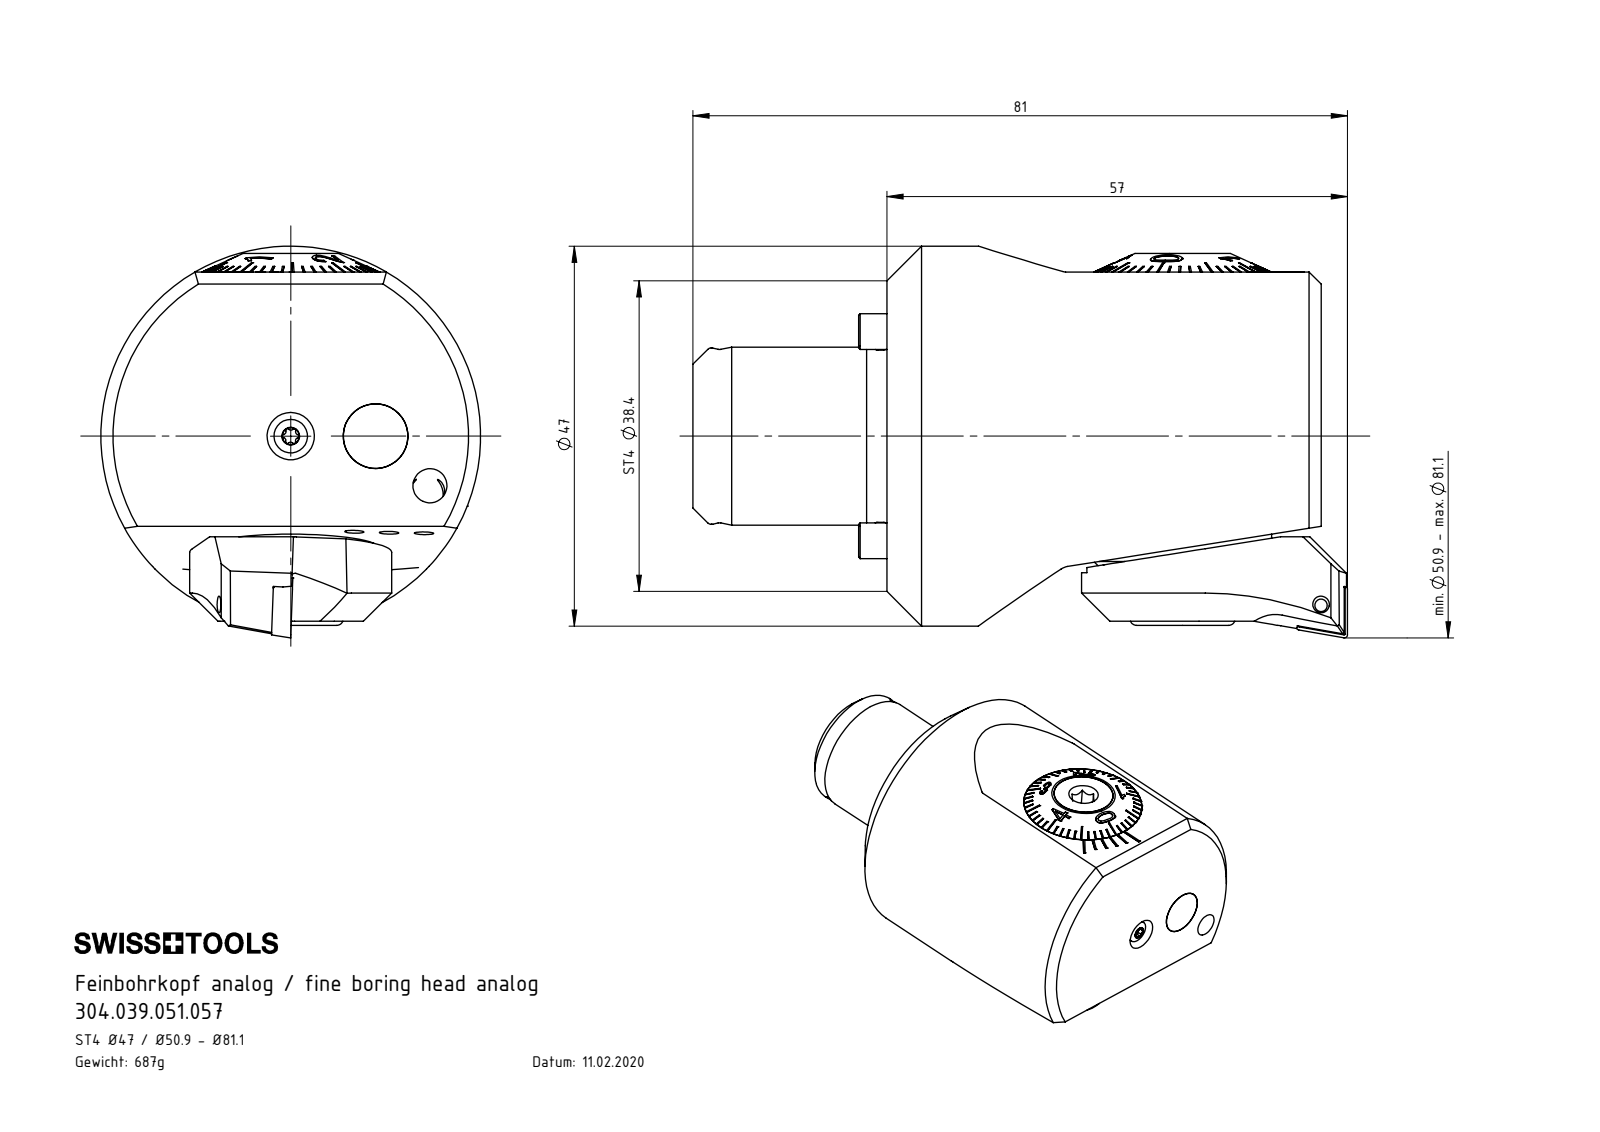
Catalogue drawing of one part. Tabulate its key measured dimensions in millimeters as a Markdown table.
| quantity | value |
| --- | --- |
| part name | F42-BG1.AA4.022; F42-BG2.014.014_A; DIN 3771 - 19x1.5; Klebstoff D8 (+8 more) |
| STEP written by | SolidWorks 2017 (CONFIG_CONTROL_DESIGN) |
| units | millimeters |
| bodies | 15 solids, 750 faces (306 planar, 154 cylindrical, 290 other) |
| overall size | 77.75 × 47 × 47 |
| volume | 85 797 mm³ |
| surface area | 26 951 mm² |
| round holes (diameter × count) | 2.1 × 3, 3.5 × 2, 4.2 × 2, 6.8 × 2, 8.5 × 2, 2.5 × 1, 3 × 1, 3.2 × 1, 3.3 × 1, 3.9 × 1, 4 × 1, 5 × 1 |
| round bosses / shafts (diameter × count) | 22 × 2, 8 × 2, 47 × 1, 21.98 × 1, 21.9 × 1, 21.8 × 1, 21.3 × 1, 18.45 × 1 |
| partial cylindrical surfaces (radius × count) | 0.5 × 7, 0.21 × 6, 0.36 × 5, 1.4 × 4, 3.2 × 3, 2 × 2, 3.48 × 2, 11.05 × 2 |
| main face-to-face distances | 53.75, 5.6, 2.2, 4.5, 1.1, 2.3, 3.3, 35.1, 30.6, 36.2 |
| hole center spacings | 13.2, 16.87, 10.5, 12.33, 26.4, 46.3, 56.88 |
